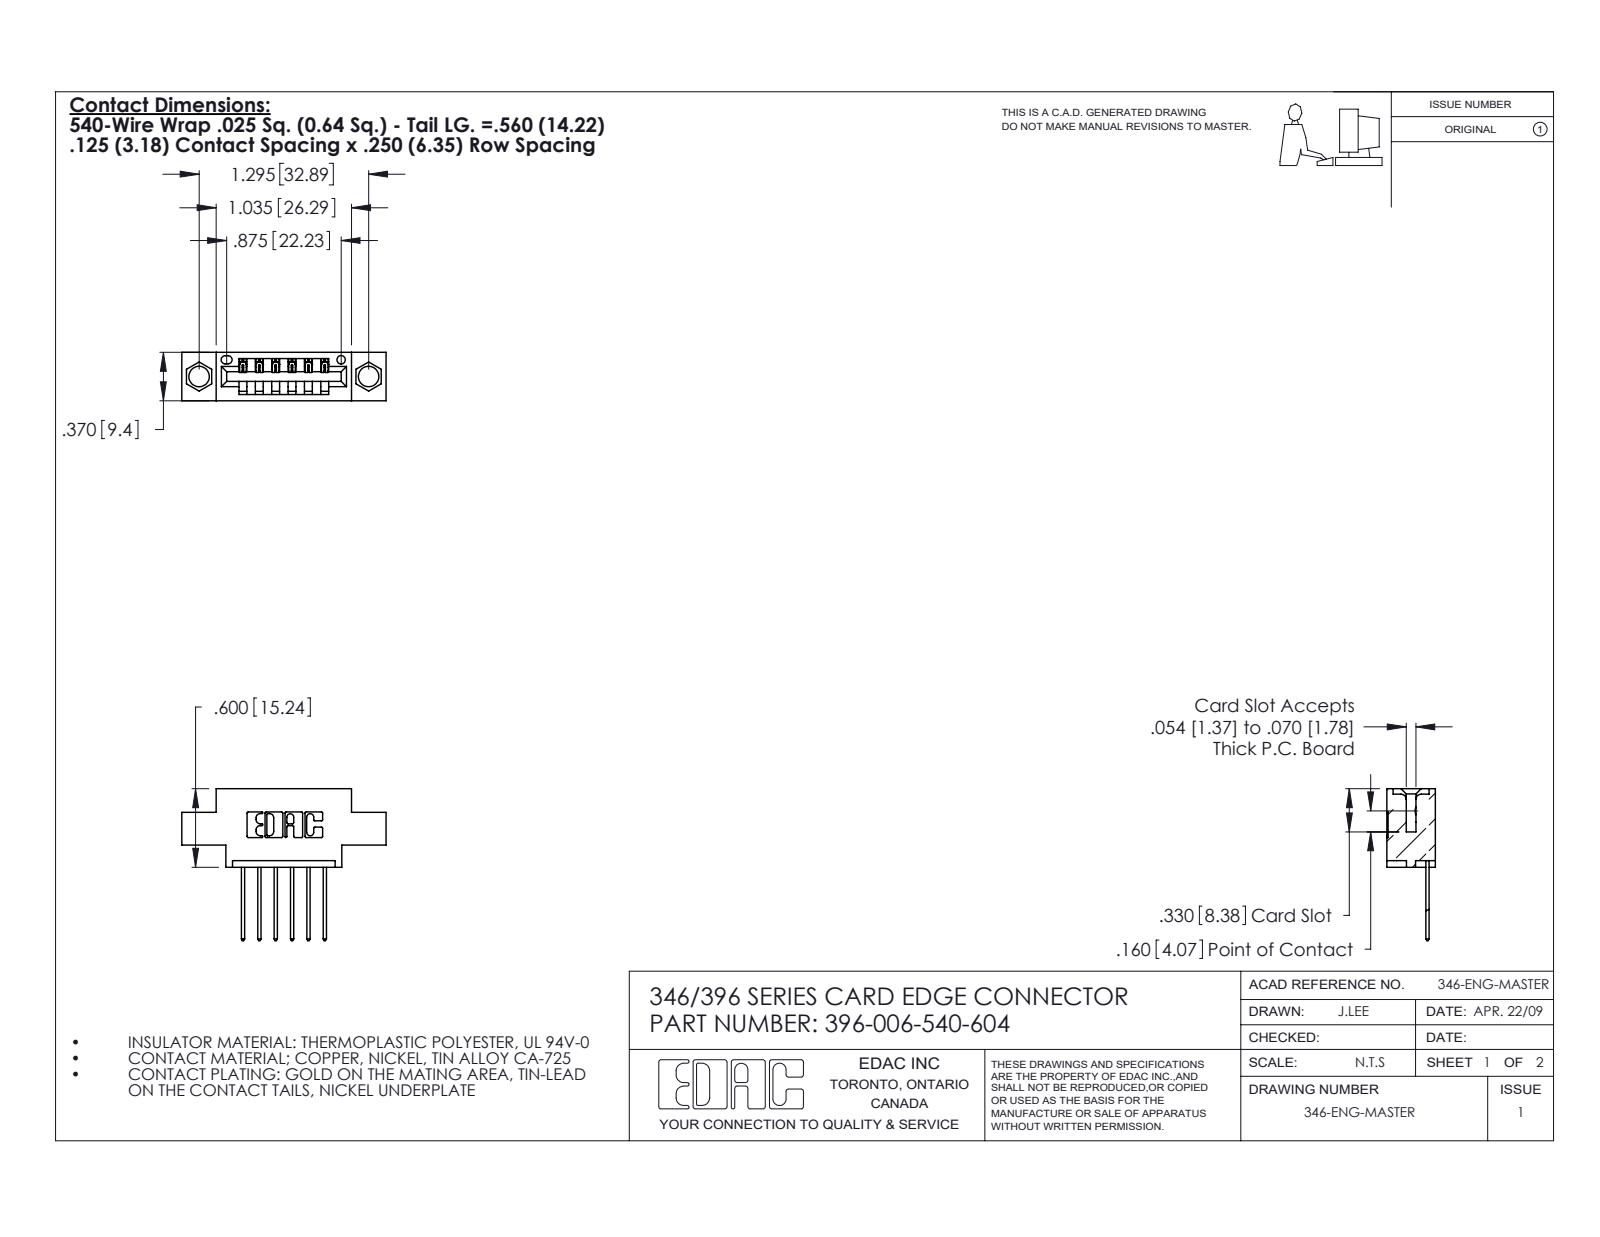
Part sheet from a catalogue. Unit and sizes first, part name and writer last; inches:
Units: inches
Overall size (bounding box): 1.56 × 1.16 × 0.37
Round holes (diameter × count): ⌀0.156 ×2, ⌀0.064 ×1
Partial cylindrical surfaces — rounded edges, fillets, slot ends (radius × count): R0.01 ×22, R0.006 ×12, R0.01 ×12, R0.007 ×6, R0.031 ×6, R0.026 ×3, R0.031 ×2, R0.04 ×2
Main face-to-face distances: 0.25, 0.37, 0.048, 0.322, 0.222, 0.072, 0.298, 0.025, 0.148, 0.1
Hole centre spacings: 0.246, 1.092, 1.295
Volume: 0.201 in³ · Surface area: 5.864 in²
Bodies: 7 solids, 488 faces (334 planar, 154 cylindrical, 0 other)
Part name (STEP PRODUCT): 346 Part_0.170 Offset - 0.156 Dia-TH; 345-292-001_345-293-140; 396-006-540-604
STEP written by: SolidWorks 2020 (CONFIG_CONTROL_DESIGN)
